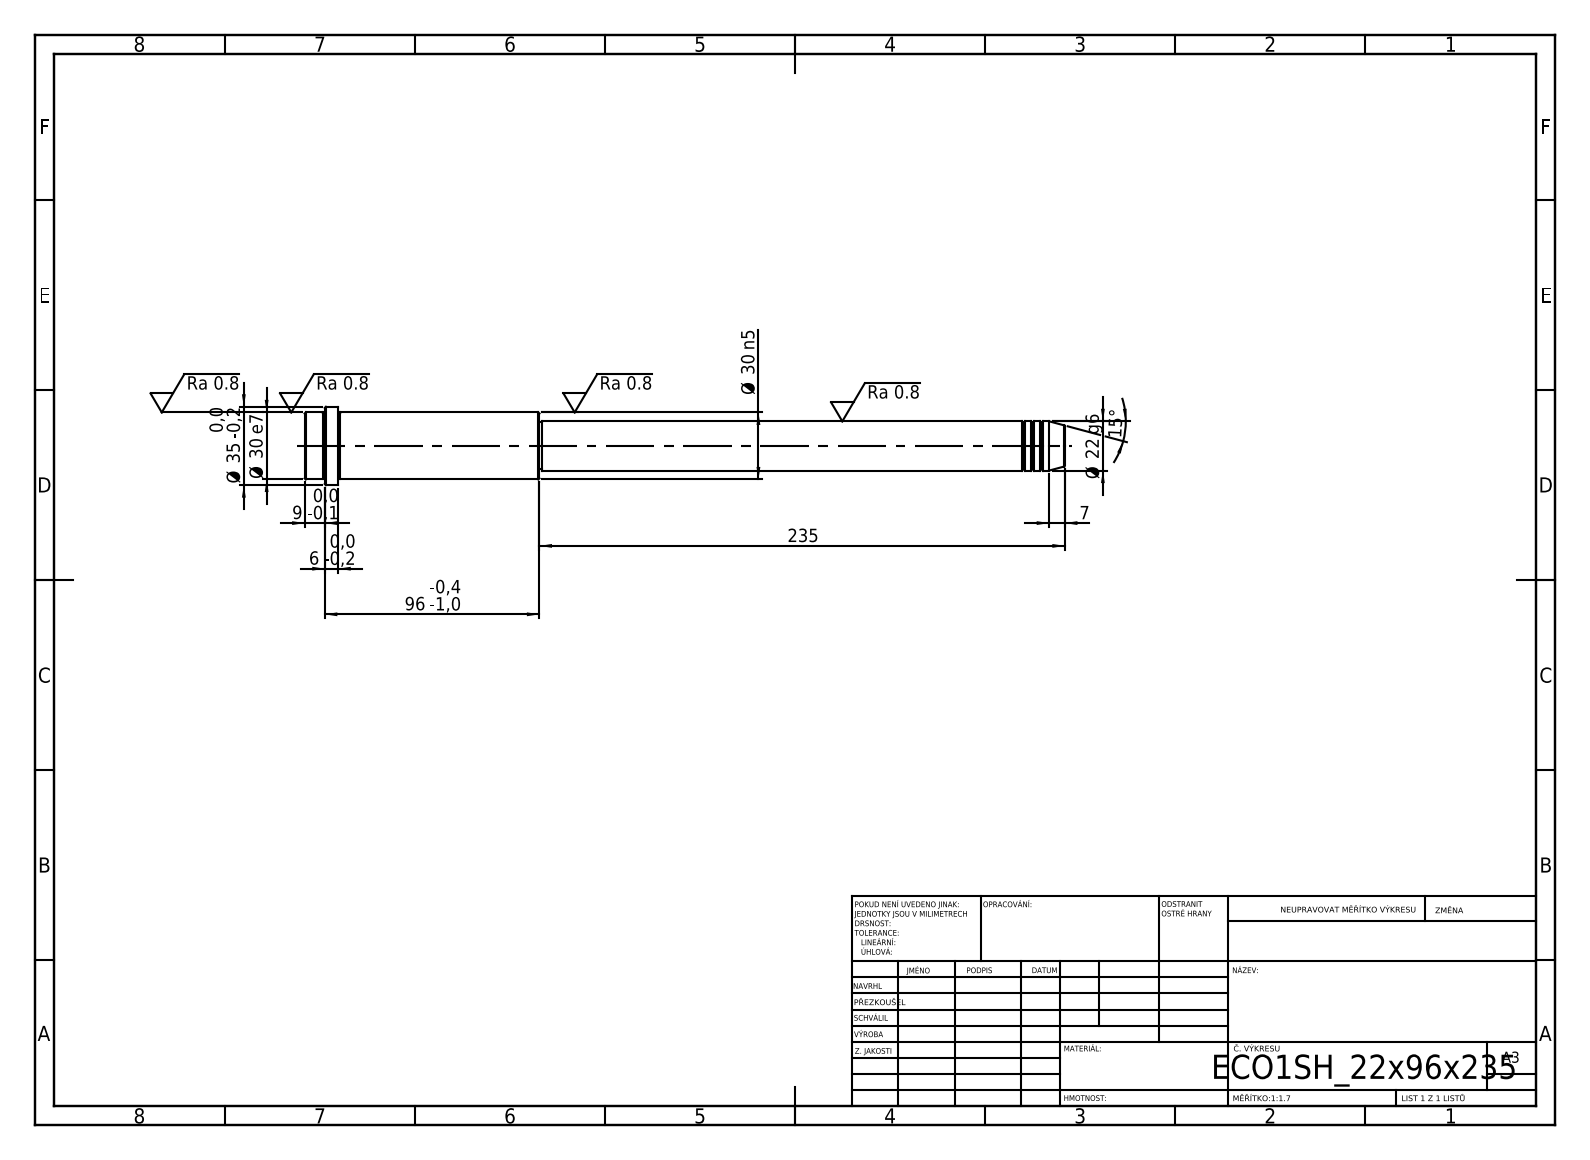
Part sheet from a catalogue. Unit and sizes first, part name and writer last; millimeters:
Units: millimetres
Overall size (bounding box): 340 × 35 × 35
Round bosses / shafts (diameter × count): ⌀35 ×1, ⌀30 ×1, ⌀22 ×1, ⌀21 ×1
Main face-to-face distances: 105, 90, 15, 235, 325, 340, 331, 96, 6, 9
Volume: 164 430 mm³ · Surface area: 28 192 mm²
Bodies: 1 solid, 52 faces (6 planar, 16 cylindrical, 30 other)
STEP written by: SolidWorks 2019 (CONFIG_CONTROL_DESIGN)
